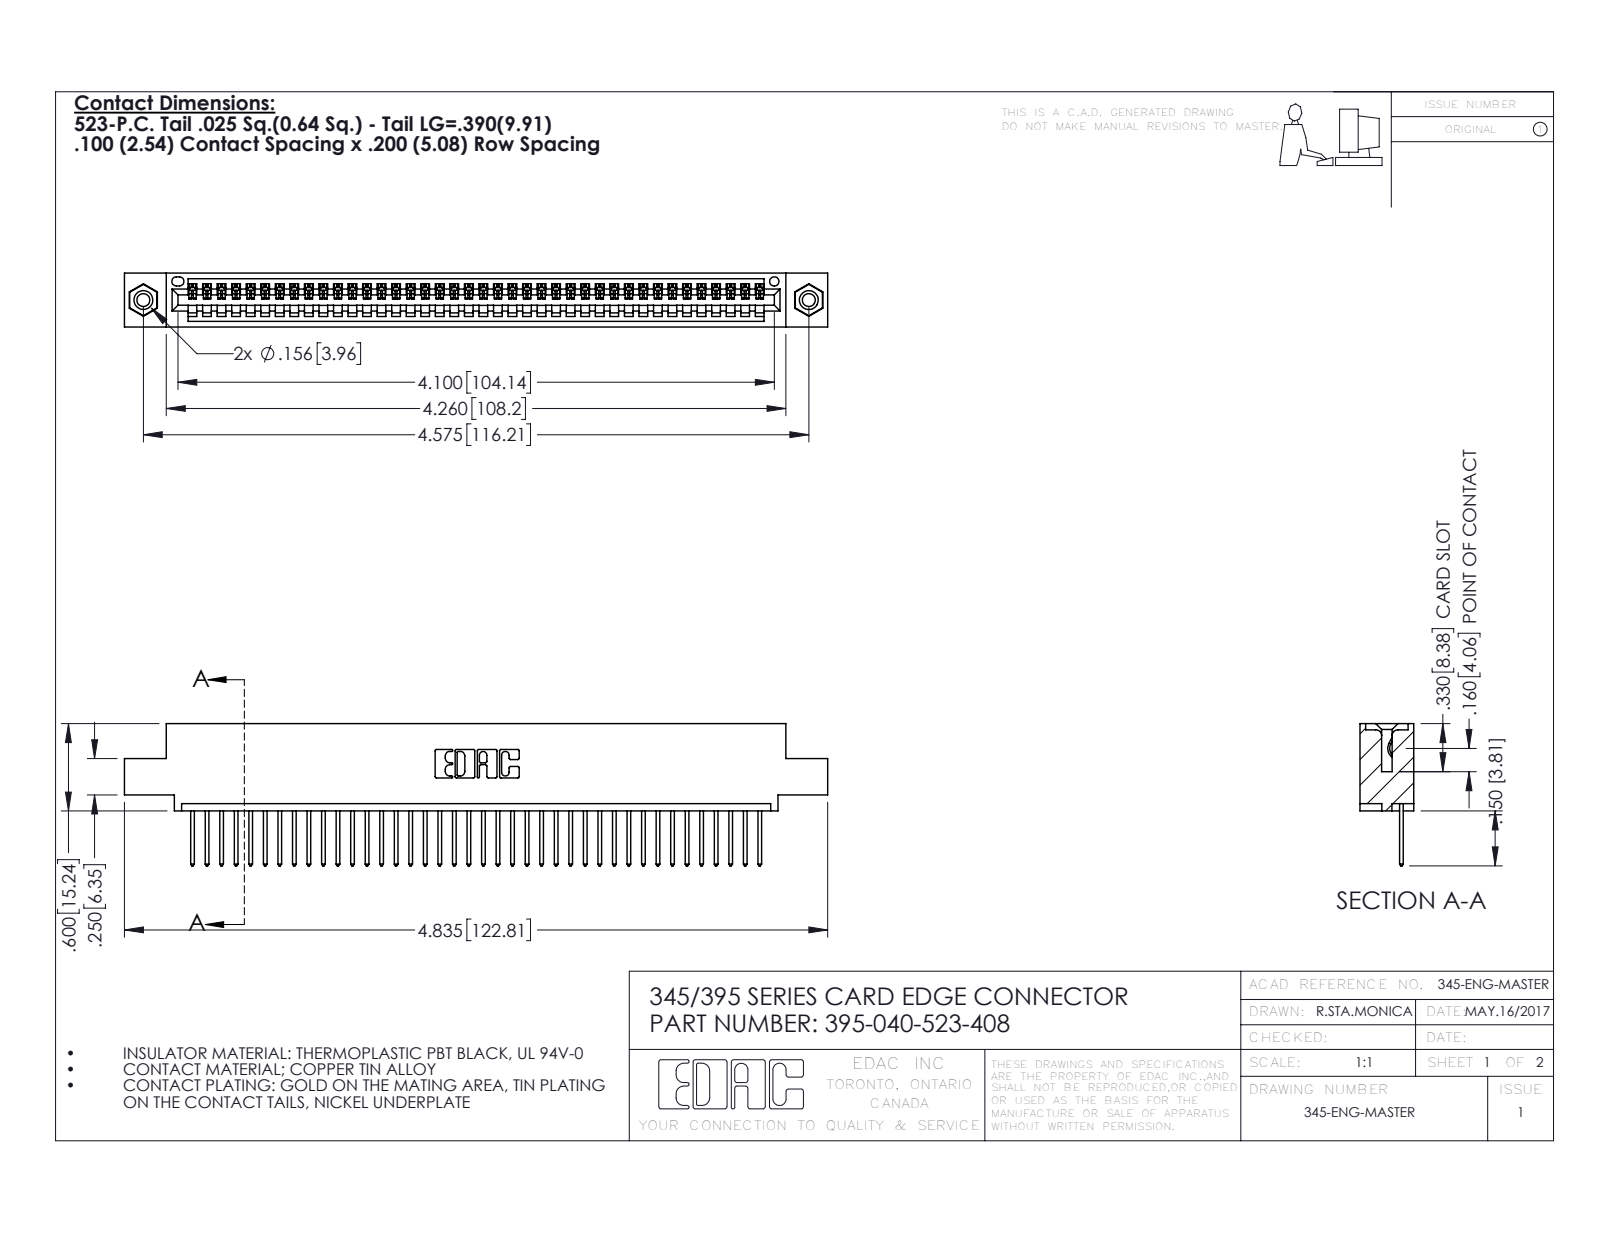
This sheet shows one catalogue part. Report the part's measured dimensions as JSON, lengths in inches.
{"part_name": "345-250-001_345-250-003-102; 345-292-001_345-293-123; 395-040-523-408; 345 Part_0.110 Offset - 0.156 Dia-TI", "step_written_by": "SolidWorks 2016 (CONFIG_CONTROL_DESIGN)", "units": "inches", "bodies": {"solids": 43, "faces": 2510, "planar": 1716, "cylindrical": 778, "other": 16}, "overall_size": [4.835, 0.977, 0.37], "volume_in3": 0.705, "surface_area_in2": 23.98, "round_holes": [[0.089, 2], [0.125, 2], [0.156, 2], [0.064, 1]], "round_bosses_or_shafts": [[0.155, 2]], "partial_cylinders_radius": [[0.006, 80], [0.01, 80], [0.01, 22], [0.007, 6], [0.031, 6], [0.026, 3], [0.031, 2], [0.04, 2]], "face_to_face_distances": [0.072, 0.298, 0.37, 0.2, 0.098, 0.272, 0.025, 0.225, 0.149, 0.072], "hole_center_spacings": [0.27, 4.339, 4.575]}
